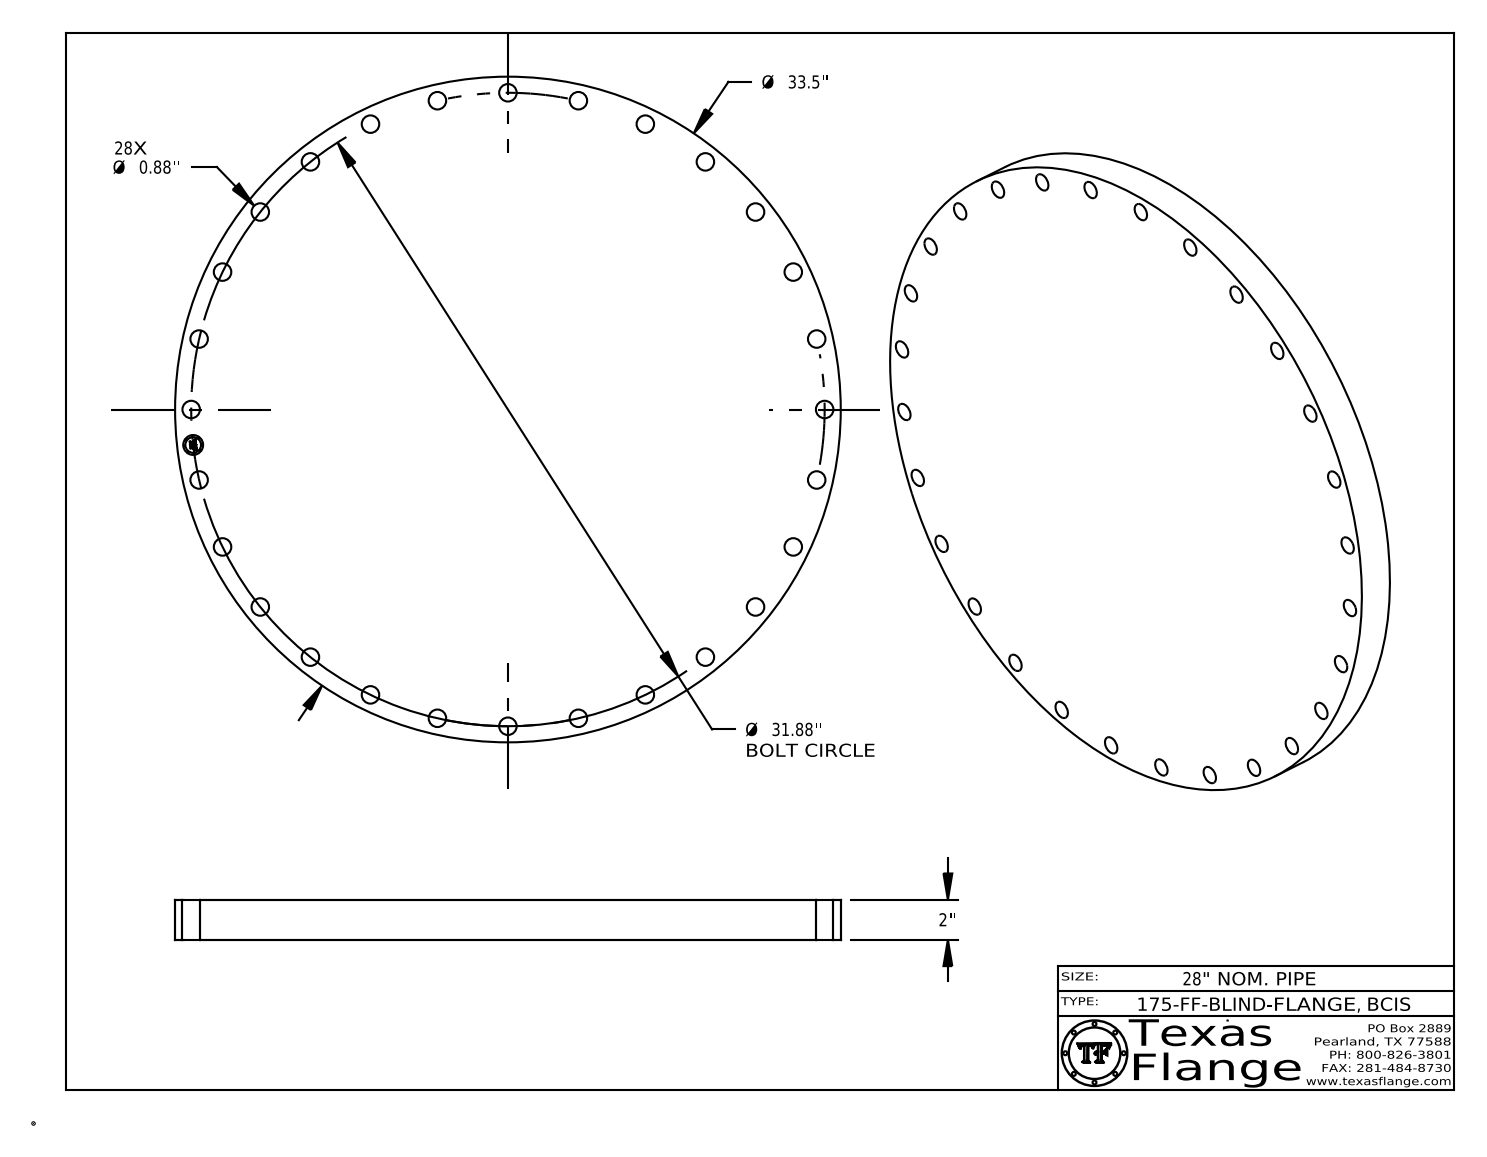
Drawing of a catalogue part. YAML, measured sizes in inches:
part_name: "175-FF-BLIND, Series BCIS"
step_written_by: "CATIA V5 STEP AP214 (AUTOMOTIVE_DESIGN)"
units: inches
bodies: {solids: 1, faces: 445, planar: 367, cylindrical: 78, other: 0}
overall_size: [33.5, 33.5, 2]
volume: 1729
surface_area: 2094
round_holes:
  - {diameter: 0.88, count: 28}
  - {diameter: 1, count: 1}
round_bosses_or_shafts:
  - {diameter: 0.061, count: 8}
  - {diameter: 33.5, count: 1}
  - {diameter: 0.788, count: 1}
face_to_face_distances: [2, 0.015, 1.985, 0.298, 0.293, 0.054, 0.193, 0.248, 0.044, 0.15]
hole_center_spacings: [30.091, 19.877, 24.925, 10.529, 13.832, 31.68, 3.57, 7.094]
